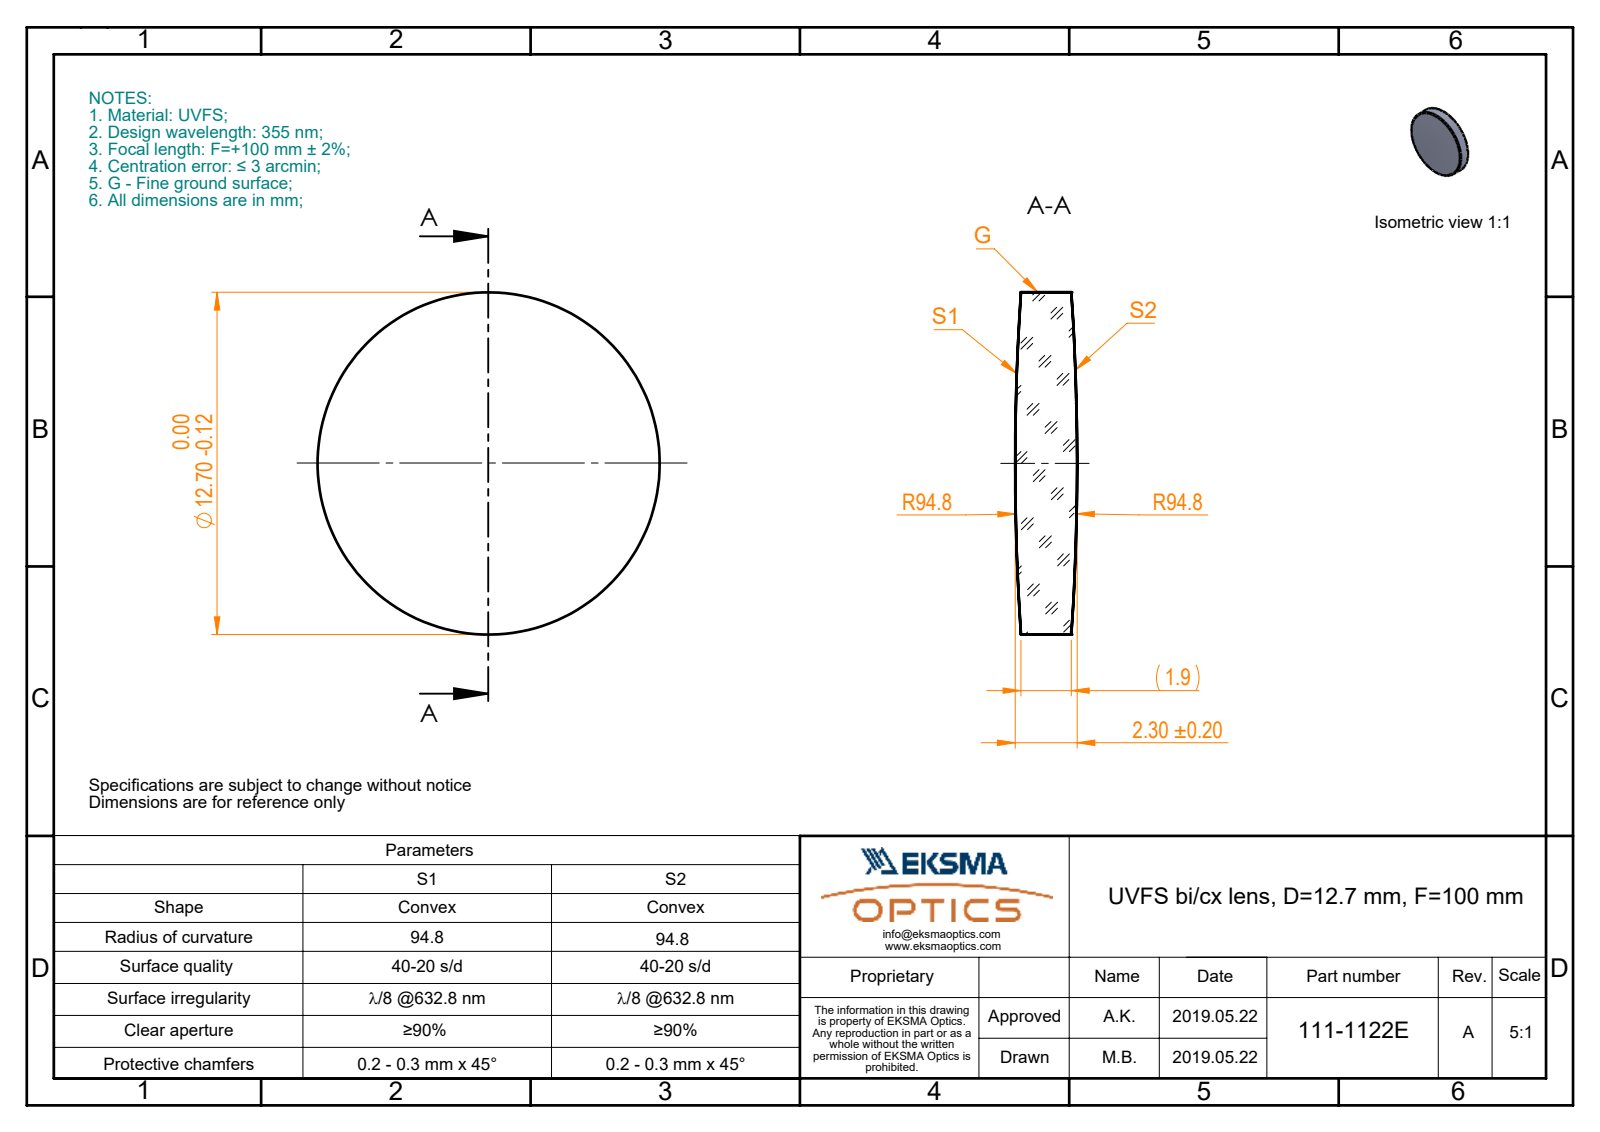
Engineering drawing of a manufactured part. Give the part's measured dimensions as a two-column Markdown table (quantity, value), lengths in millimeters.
| quantity | value |
| --- | --- |
| part name | 111-1122E UVFS bi-cx 12.7 F100 |
| STEP written by | SolidWorks 2017 (CONFIG_CONTROL_DESIGN) |
| units | millimeters |
| bodies | 1 solid, 6 faces (0 planar, 2 cylindrical, 4 other) |
| overall size | 12.7 × 12.7 × 2.3 |
| volume | 264 mm³ |
| surface area | 328 mm² |
| round bosses / shafts (diameter × count) | 12.7 × 1 |
